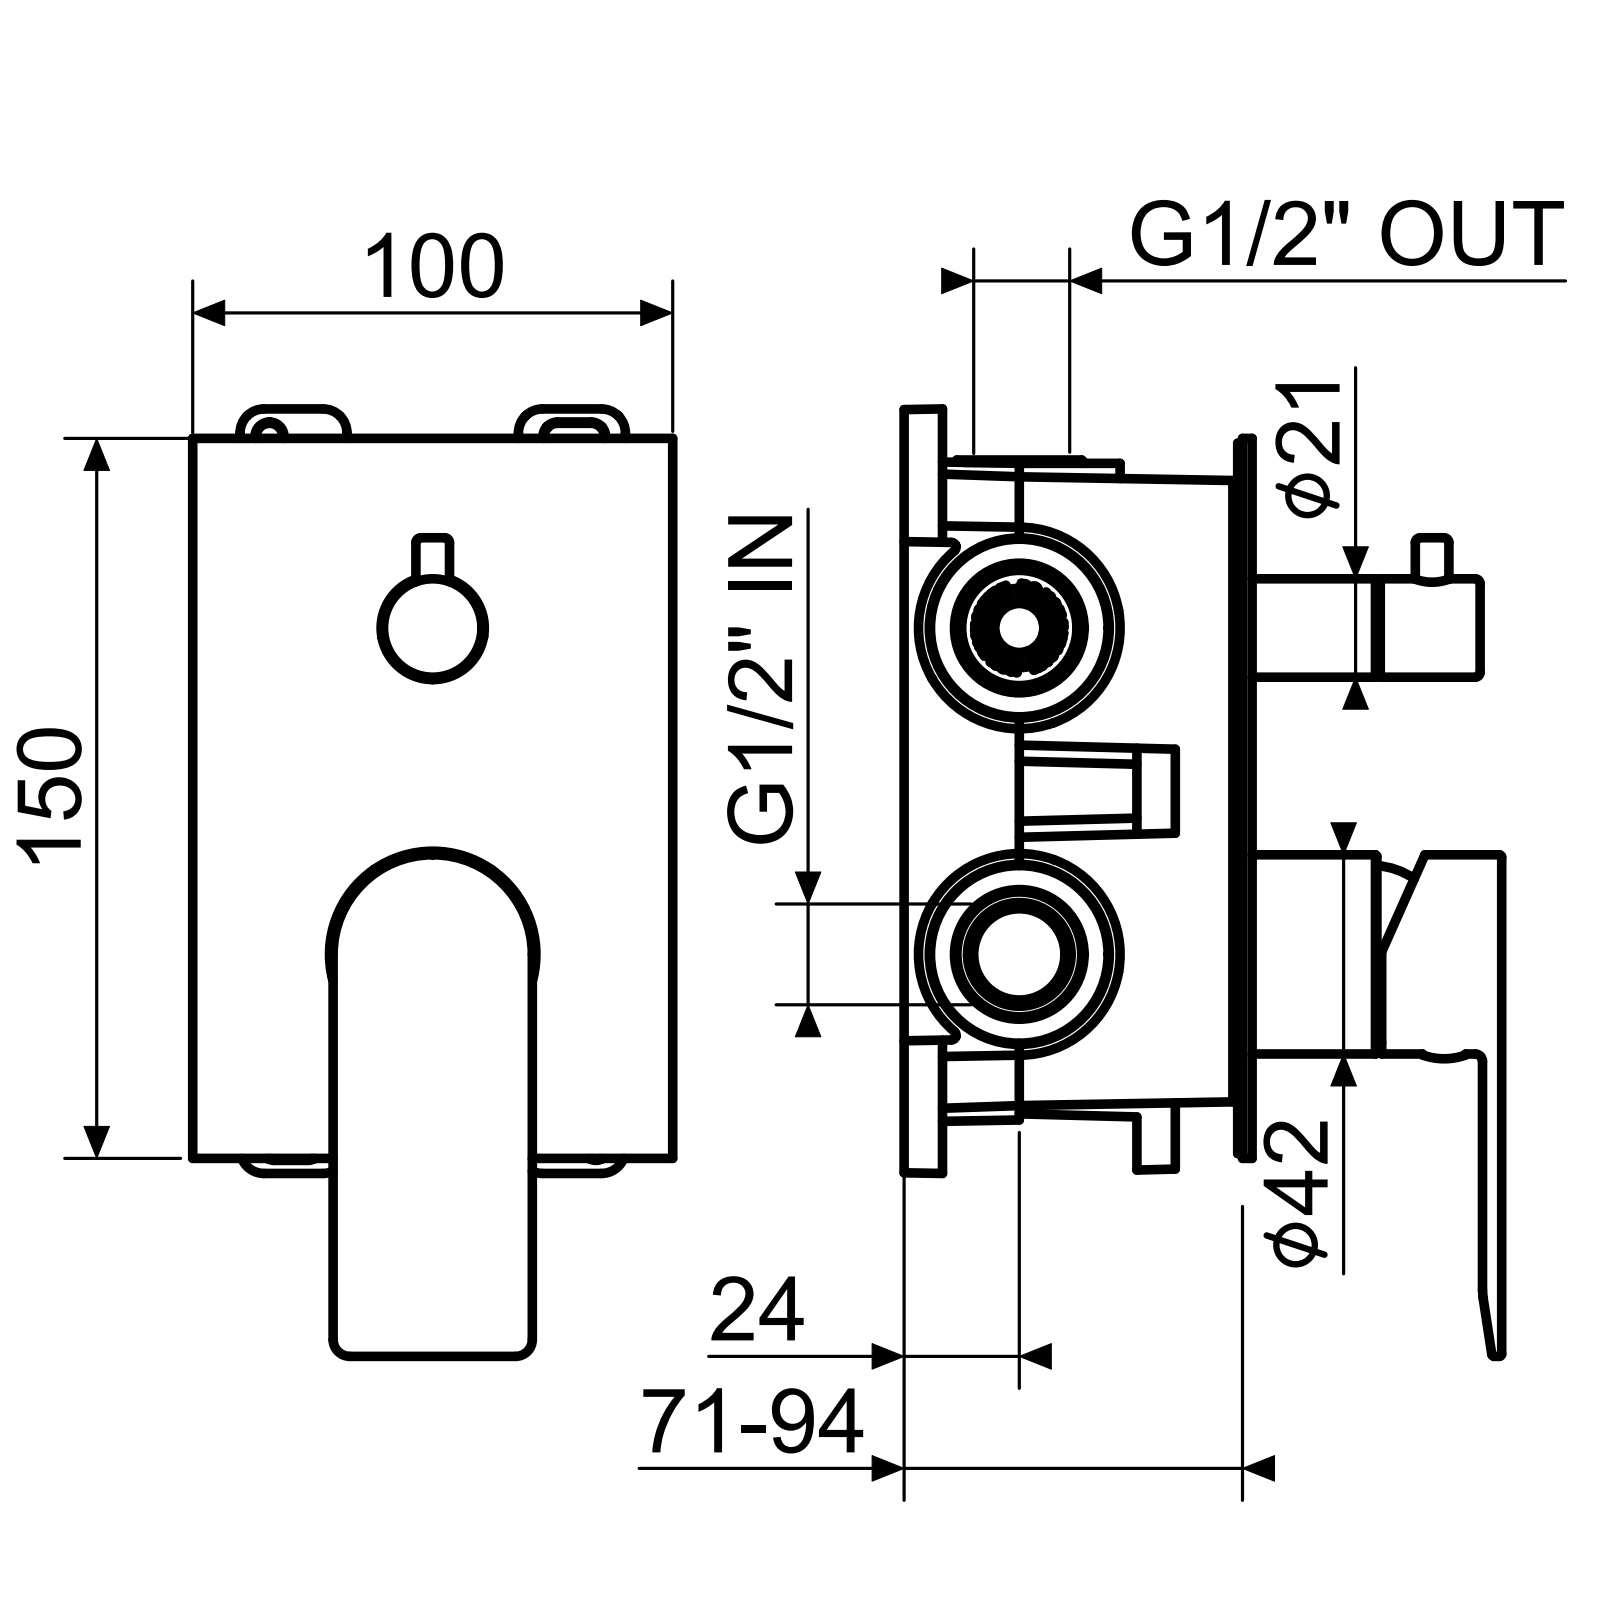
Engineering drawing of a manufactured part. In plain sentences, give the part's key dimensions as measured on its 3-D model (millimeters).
The part is named "SINMAC0008_AF0; SCCMAC0005; AAYA005C001; SPLMAC0001 (+8 more)". Its 3-D file was written by "CREO PARAMETRIC BY PTC INC, 2020281 (CONFIG_CONTROL_DESIGN)". It is 10 solids with 298 faces: 80 planar, 85 cylindrical and 133 other. Overall it measures 191.25 by 100 by 66.5 millimeters. Its volume is 59 303 cubic millimeters and its surface area 66 973 square millimeters. Round holes: 2 of diameter 4.2, 1 of diameter 5, 1 of diameter 5.2, 1 of diameter 6.5, 1 of diameter 7.5, 1 of diameter 8, 1 of diameter 12, 1 of diameter 14, 1 of diameter 18, 1 of diameter 21.5, 1 of diameter 22, 1 of diameter 25. Round bosses or shafts: 1 of diameter 49, 1 of diameter 42, 1 of diameter 41.5, 1 of diameter 34, 1 of diameter 27.5, 1 of diameter 20.5, 1 of diameter 7, 1 of diameter 5. Partial cylindrical surfaces (rounded edges, fillets, slot ends): 6 of radius 0.5, 4 of radius 1, 3 of radius 10, 2 of radius 0.3, 2 of radius 1.5, 2 of radius 3.5. The main face-to-face distances are 2, 55.6, 53.6, 4, 6, 2.4, 59.6, 27.1, 57.2, 53.2. The hole center spacings are 4.1, 68.
